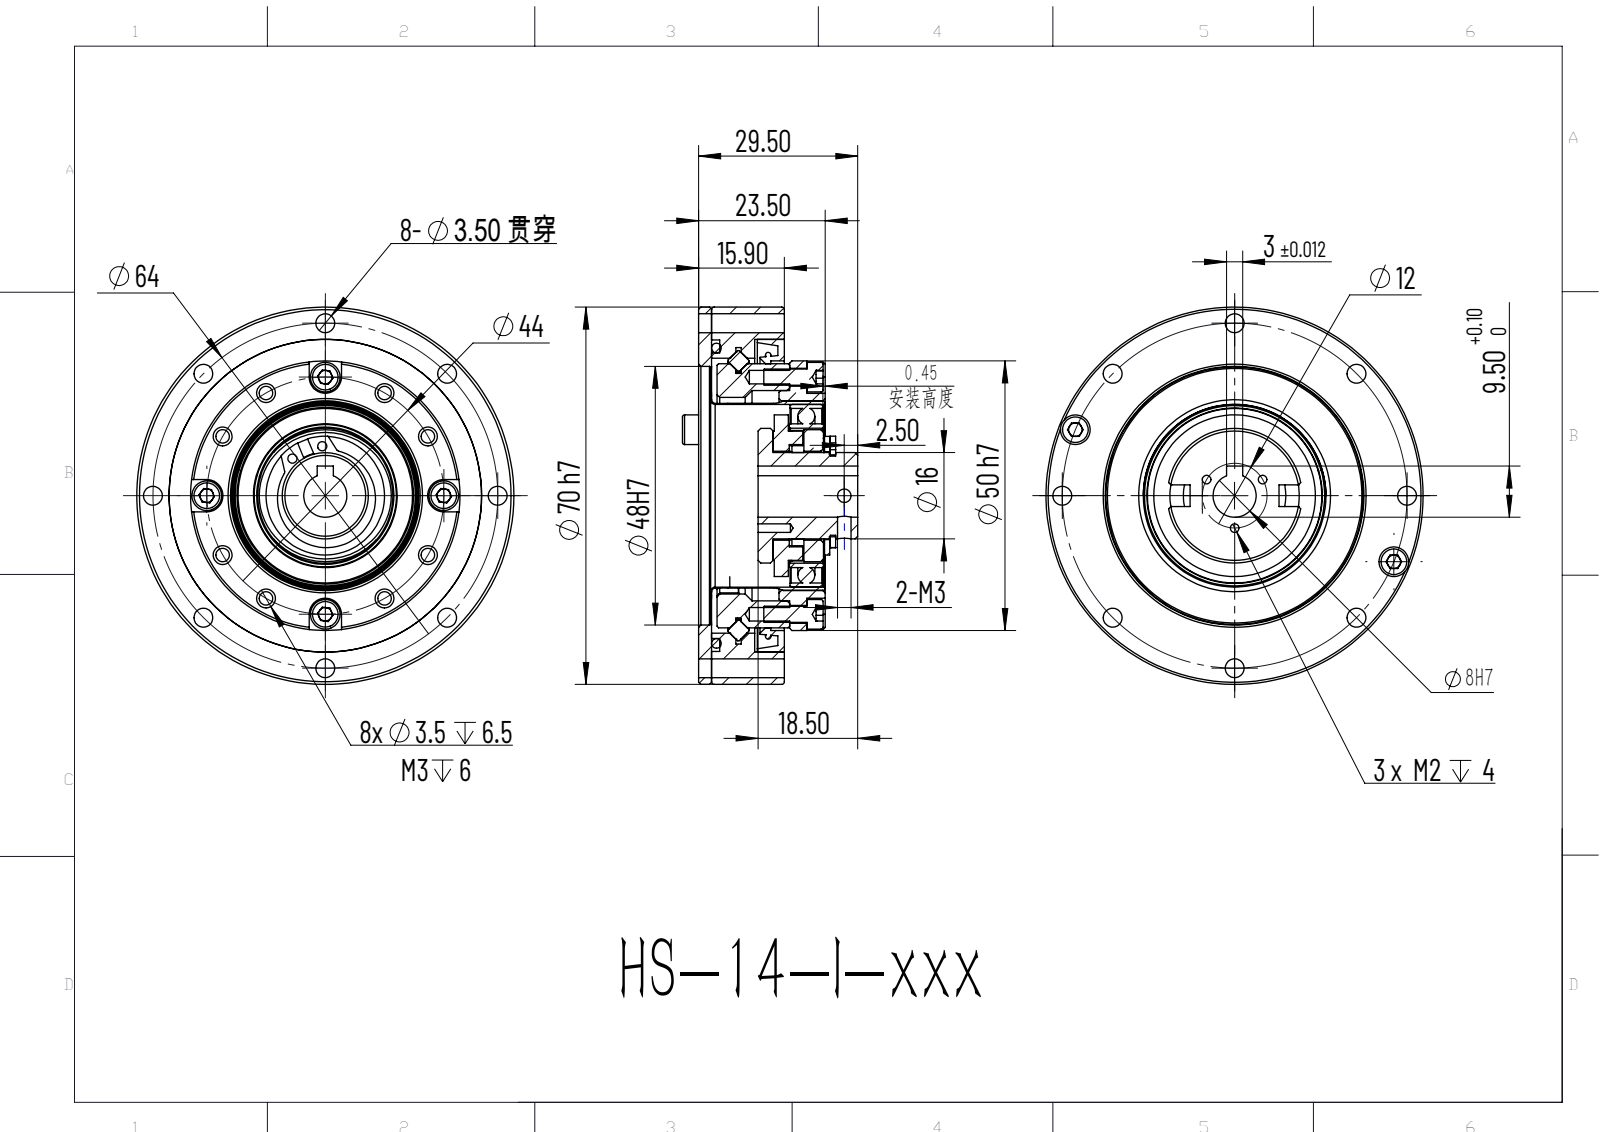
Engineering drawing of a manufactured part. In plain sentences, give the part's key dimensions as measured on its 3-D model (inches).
The part is named "HS-14-I; hexagon socket head cap screws gb_GB_FASTENER_SCREWS_HSHCS M3X8-C; ????-STXB-14050; 14-100??????_?? <1> (+8 more)". Its 3-D file was written by "ONSHAPE BY PTC INC, 1.201 (AP242_MANAGED_MODEL_BASED_3D_ENGINEERING_MIM_LF)". It is 101 solids with 901 faces: 460 planar, 253 cylindrical and 188 other. Overall it measures 2.756 by 2.756 by 1.281 inches. Its volume is 3.173 cubic inches and its surface area 79.86 square inches. Round holes: 18 of diameter 0.138, 16 of diameter 0.098, 4 of diameter 0.063, 4 of diameter 0.134, 2 of diameter 0.067, 1 of diameter 0.094, 1 of diameter 0.165, 1 of diameter 0.315, 1 of diameter 0.579, 1 of diameter 0.642, 1 of diameter 0.65, 1 of diameter 0.987. Round bosses or shafts: 46 of diameter 0.118, 6 of diameter 0.217, 1 of diameter 2.756, 1 of diameter 2.087, 1 of diameter 1.929, 1 of diameter 1.787, 1 of diameter 1.386, 1 of diameter 1.35. Partial cylindrical surfaces (rounded edges, fillets, slot ends): 40 of radius 0.06, 4 of radius 0.118, 2 of radius 0.008, 2 of radius 0.02, 1 of radius 0.374, 1 of radius 0.435. The main face-to-face distances are 0.531, 0.039, 0.094, 0.626, 0.256, 0.665, 0.571, 0.118, 0.11, 0.315. The hole center spacings are 0.866, 1.225, 1.5, 1.673, 1.26, 1.331, 0.448, 0.479.
